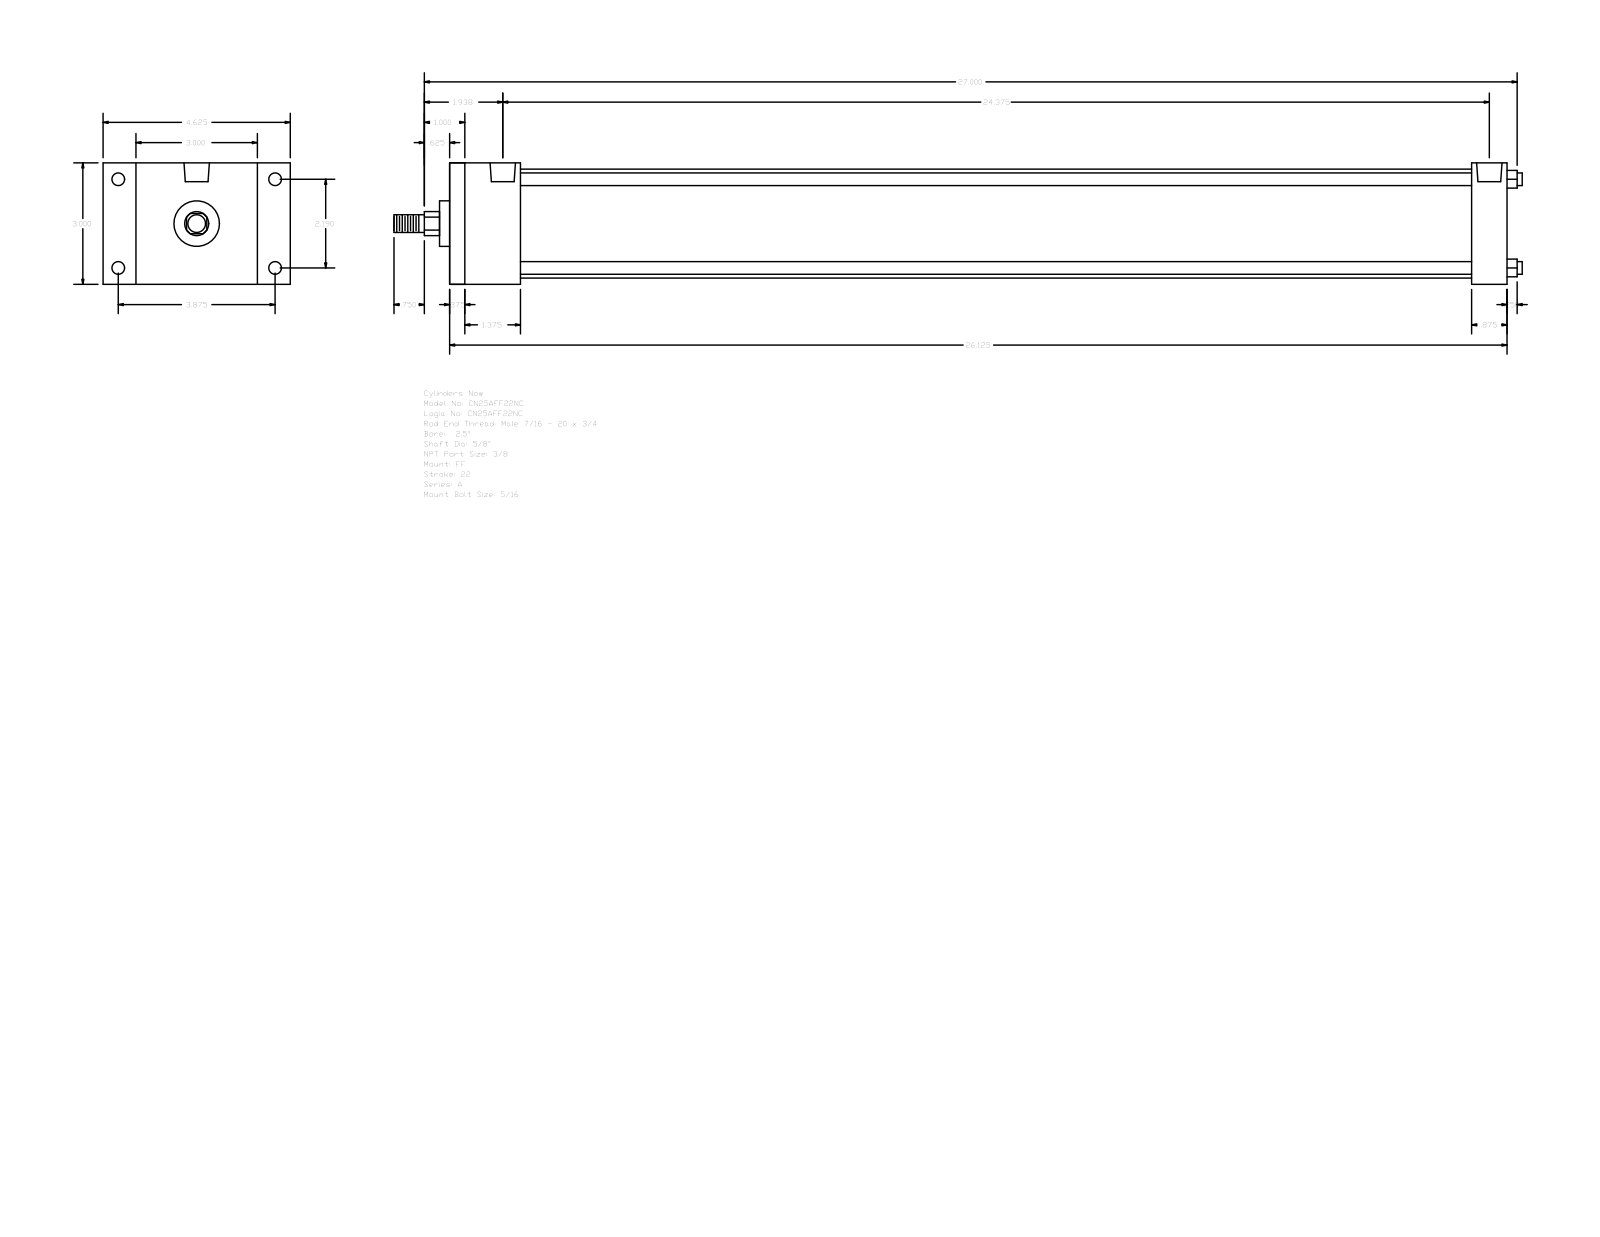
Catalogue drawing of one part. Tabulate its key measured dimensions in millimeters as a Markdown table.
| quantity | value |
| --- | --- |
| part name | A_FF__0250_0.625 |
| STEP written by | GSSL Pune (CONFIG_CONTROL_DESIGN) |
| units | millimeters |
| bodies | 0 solids, 92 faces (64 planar, 28 cylindrical, 0 other) |
| overall size | 708.02 × 117.47 × 76.2 |
| round holes (diameter × count) | 5.56 × 4, 7.94 × 4, 15.93 × 2 |
| round bosses / shafts (diameter × count) | 7.94 × 4, 68.33 × 1, 28.57 × 1, 15.88 × 1, 11.11 × 1 |
| partial cylindrical surfaces (radius × count) | 7.54 × 1 |
| main face-to-face distances | 76.2, 663.57, 9.52, 654.05, 44.45, 34.93, 641.35, 631.83, 596.9, 619.12 |
| hole center spacings | 2.38, 55.62, 98.42, 113.05, 621.51, 623.89, 619.13 |
